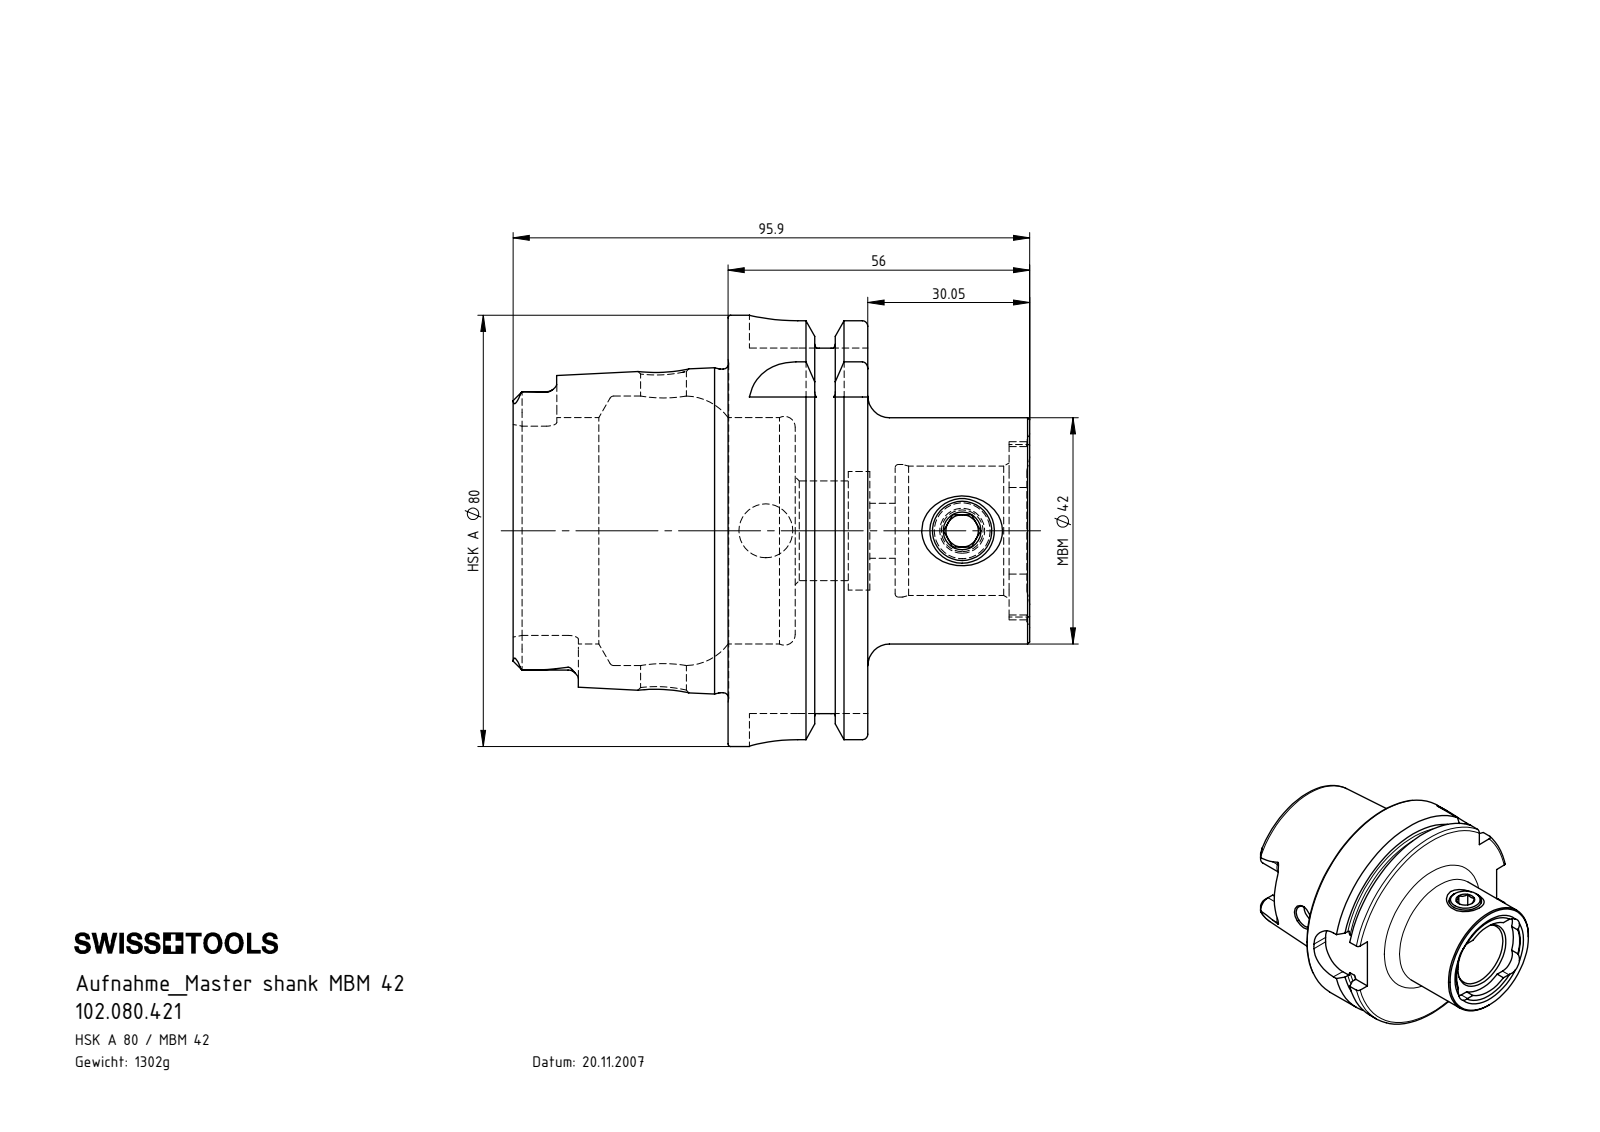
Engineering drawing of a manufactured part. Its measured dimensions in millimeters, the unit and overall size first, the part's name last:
Units: millimetres
Overall size (bounding box): 95.9 × 80 × 80
Round holes (diameter × count): ⌀6 ×1, ⌀8.5 ×1, ⌀10 ×1, ⌀10.2 ×1, ⌀11 ×1, ⌀18.5 ×1, ⌀22 ×1, ⌀24 ×1, ⌀24.6 ×1, ⌀42 ×1, ⌀50 ×1
Round bosses / shafts (diameter × count): ⌀80 ×1, ⌀69.95 ×1, ⌀60.06 ×1, ⌀12 ×1
Partial cylindrical surfaces — rounded edges, fillets, slot ends (radius × count): R1.9 ×6, R3.88 ×4, R5.2 ×4, R9 ×4, R14.9 ×1, R16.52 ×1
Main face-to-face distances: 25.95, 12.45, 13.5, 39.9, 52.35, 65.85, 31, 56, 3.85, 67.8
Hole centre spacings: 36.45
Volume: 165 818 mm³ · Surface area: 39 832 mm²
Bodies: 2 solids, 224 faces (70 planar, 66 cylindrical, 88 other)
Part name (STEP PRODUCT): 102.080.421; MB4-ER1.001.013_A; HA8-MB4.K01.056_B_Fertigbearbeitung
STEP written by: SolidWorks 2017 (CONFIG_CONTROL_DESIGN)
